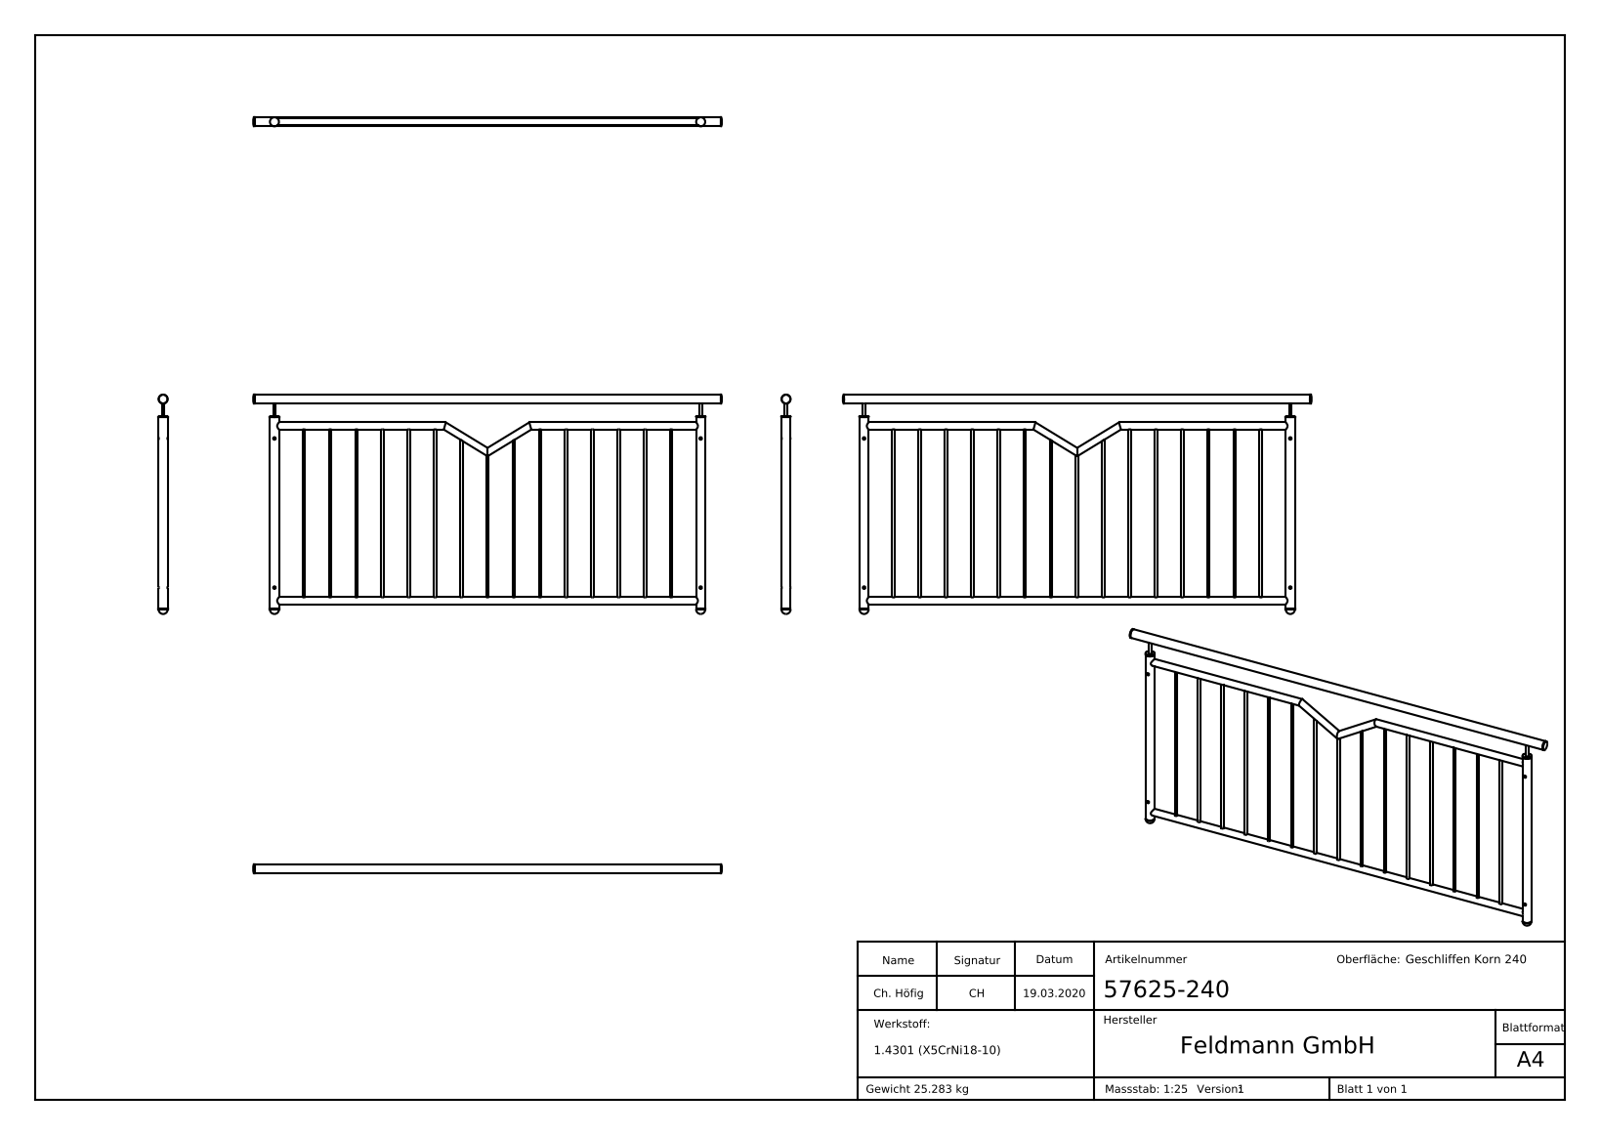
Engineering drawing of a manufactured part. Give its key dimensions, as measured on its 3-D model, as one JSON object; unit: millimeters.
{"part_name": "576XX-240 Teil1_57625-240 Teil1; Stopfen Konfig; 576XX-240 Teil1; 576XX-240 Teil2 (+7 more)", "step_written_by": "SolidWorks 2015 (CONFIG_CONTROL_DESIGN)", "units": "millimeters", "bodies": {"solids": 10, "faces": 6690, "planar": 3206, "cylindrical": 1052, "other": 2432}, "overall_size": [16102.4, 8000, 8000], "volume_mm3": 3200000, "surface_area_mm2": 2289000, "round_holes": [[12, 4], [29.7, 4], [38.4, 3], [6.8, 2], [34.5, 2], [34.6, 1]], "round_bosses_or_shafts": [[12, 17], [33.7, 4], [42.4, 3], [37.5, 3], [8, 2], [6, 2]], "partial_cylinders_radius": [[2, 4], [19.4, 3], [17.35, 2], [19.3, 1]], "face_to_face_distances": [13, 5, 8, 890.6, 898.6, 903.6, 18.7, 18.75, 2186, 18.76], "hole_center_spacings": [2000, 700, 2118.96, 126.2, 820, 946.2]}
